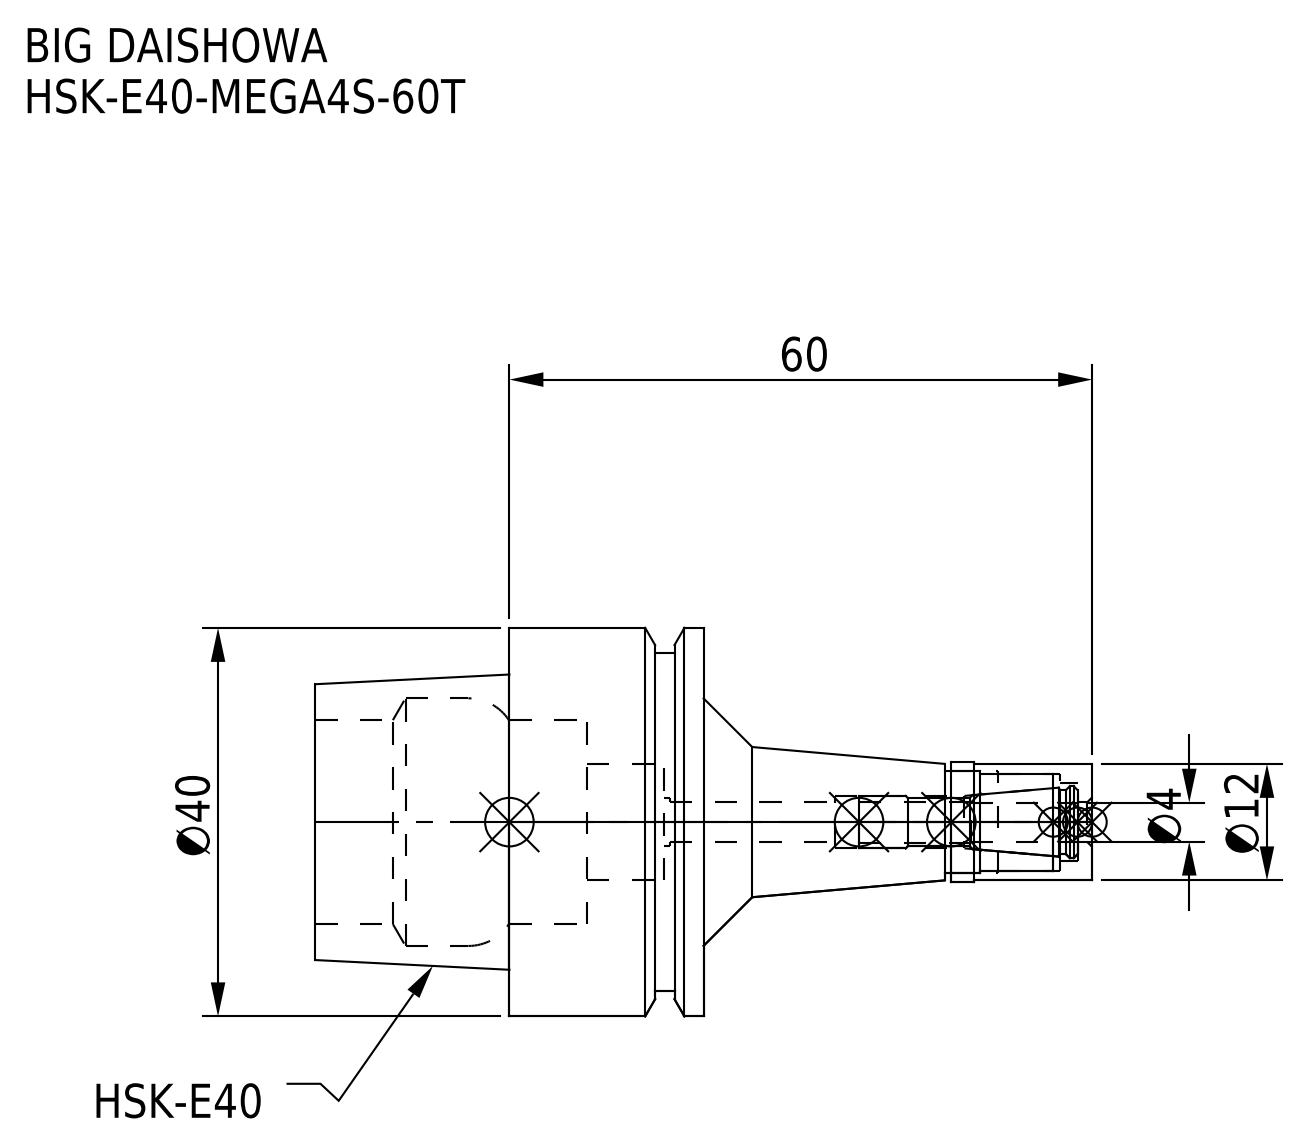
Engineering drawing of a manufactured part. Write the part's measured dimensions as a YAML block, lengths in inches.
part_name: "HSK-E40-MEGA4S-60T_1.stp; HSK-E40-MEGA4S-60T; HSK-E40-MEGA4S-60T-040.stp; MGN4S_1.stp (+3 more)"
step_written_by: "SolidWorks 2019 (CONFIG_CONTROL_DESIGN)"
units: inches
bodies: {solids: 2, faces: 74, planar: 18, cylindrical: 38, other: 18}
overall_size: [3.15, 1.575, 1.575]
volume: 1.891
surface_area: 19.61
round_holes:
  - {diameter: 0.161, count: 1}
  - {diameter: 0.197, count: 1}
  - {diameter: 0.213, count: 1}
  - {diameter: 0.315, count: 1}
  - {diameter: 0.394, count: 1}
  - {diameter: 0.413, count: 1}
  - {diameter: 0.472, count: 1}
  - {diameter: 0.827, count: 1}
  - {diameter: 1.004, count: 1}
round_bosses_or_shafts:
  - {diameter: 1.575, count: 1}
  - {diameter: 1.37, count: 1}
  - {diameter: 0.484, count: 1}
face_to_face_distances: [0.787, 1.575, 0.474, 0.313, 1.1, 0.118, 0.591, 0.669, 0.159, 0.315]
